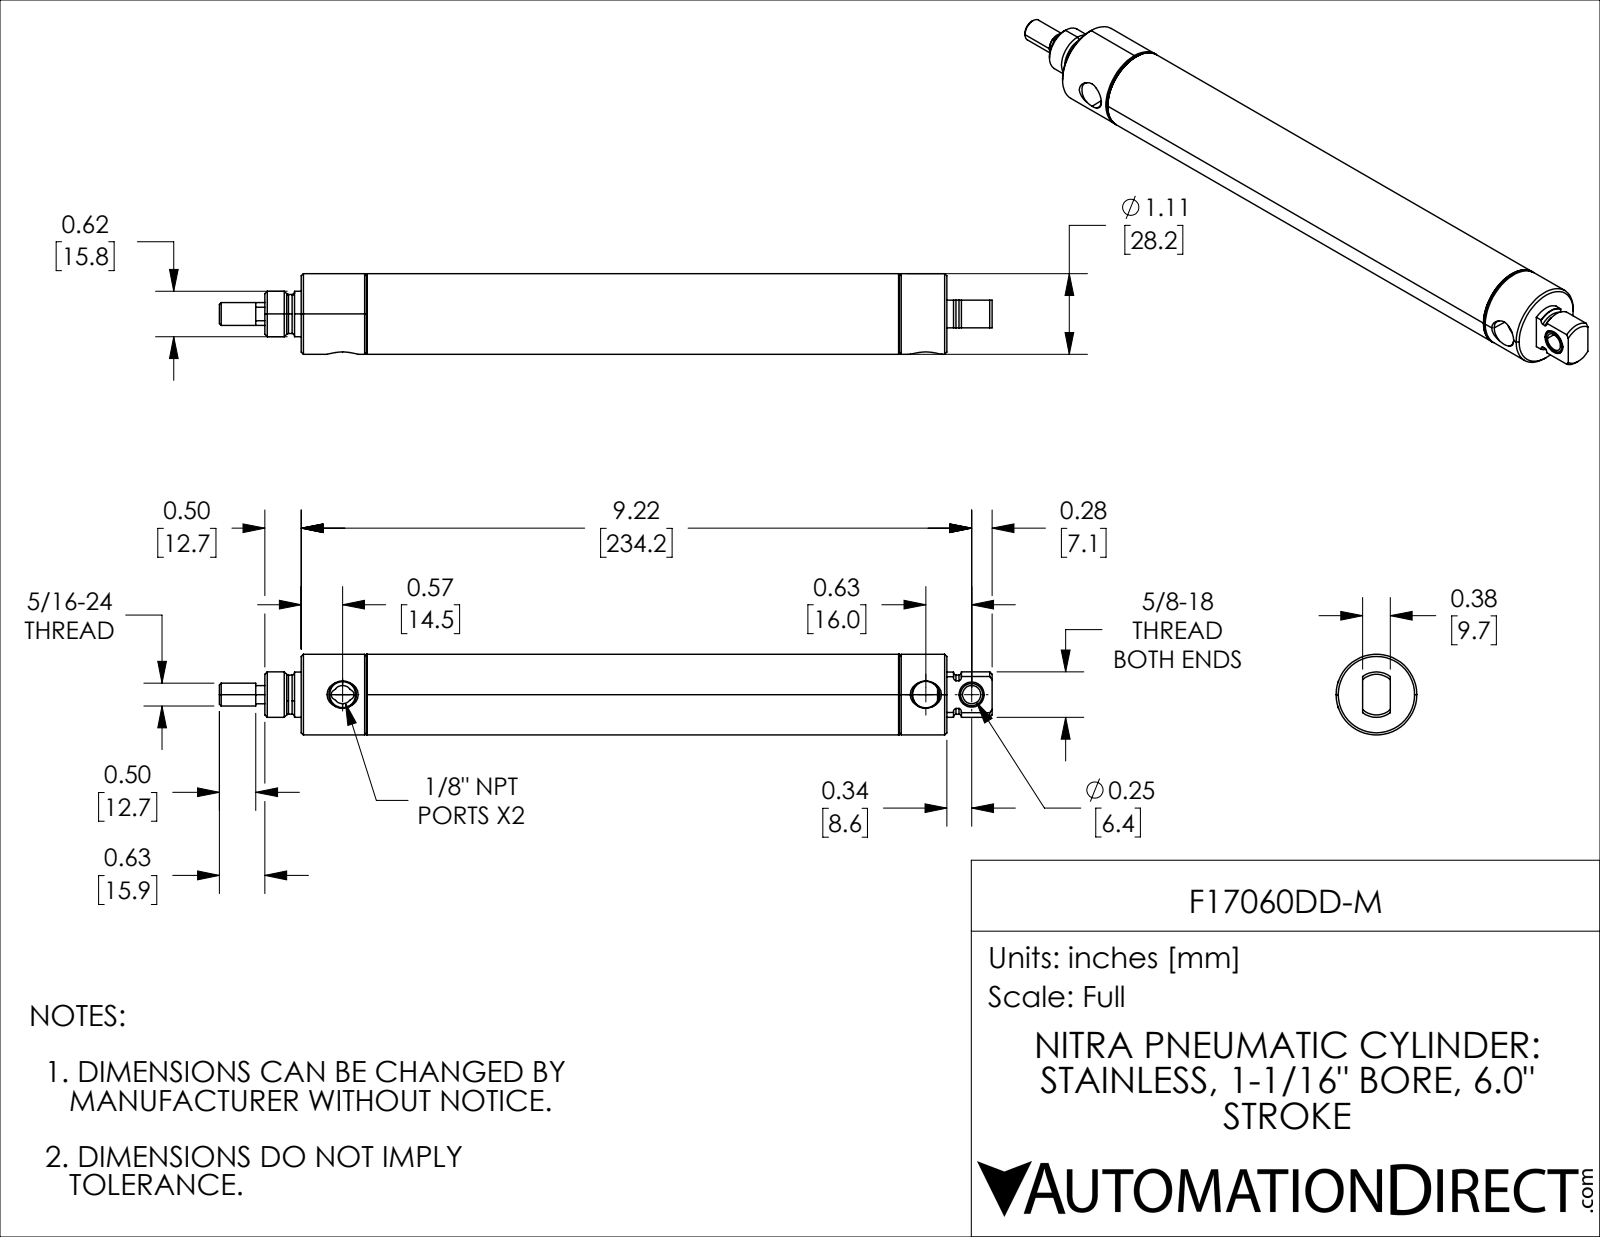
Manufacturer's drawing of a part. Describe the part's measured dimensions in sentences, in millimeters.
The part is named "F17060DD-M_7; F17060DD-M; F17060DD-M_9; F17060DD-M_5 (+2 more)". Its 3-D file was written by "SolidWorks 2021 (CONFIG_CONTROL_DESIGN)". It is 5 solids with 156 faces: 30 planar, 58 cylindrical and 68 other. Overall it measures 269.88 by 28.19 by 28.19 millimeters. Its volume is 59 773 cubic millimeters and its surface area 52 470 square millimeters. Round holes: 1 of diameter 6.38, 1 of diameter 8.53, 1 of diameter 8.78, 1 of diameter 9.25, 1 of diameter 9.53, 1 of diameter 19.05, 1 of diameter 25.7. Round bosses or shafts: 1 of diameter 28.19, 1 of diameter 27.23, 1 of diameter 15.88, 1 of diameter 15.81, 1 of diameter 13.68, 1 of diameter 7.94, 1 of diameter 7.92. Partial cylindrical surfaces (rounded edges, fillets, slot ends): 1 of radius 3.17, 1 of radius 6.84. The main face-to-face distances are 22.22, 152.4, 174.62, 196.95, 44.55, 22.33, 28.58, 180.98, 203.2, 225.53. The hole center spacings are 16.01.
